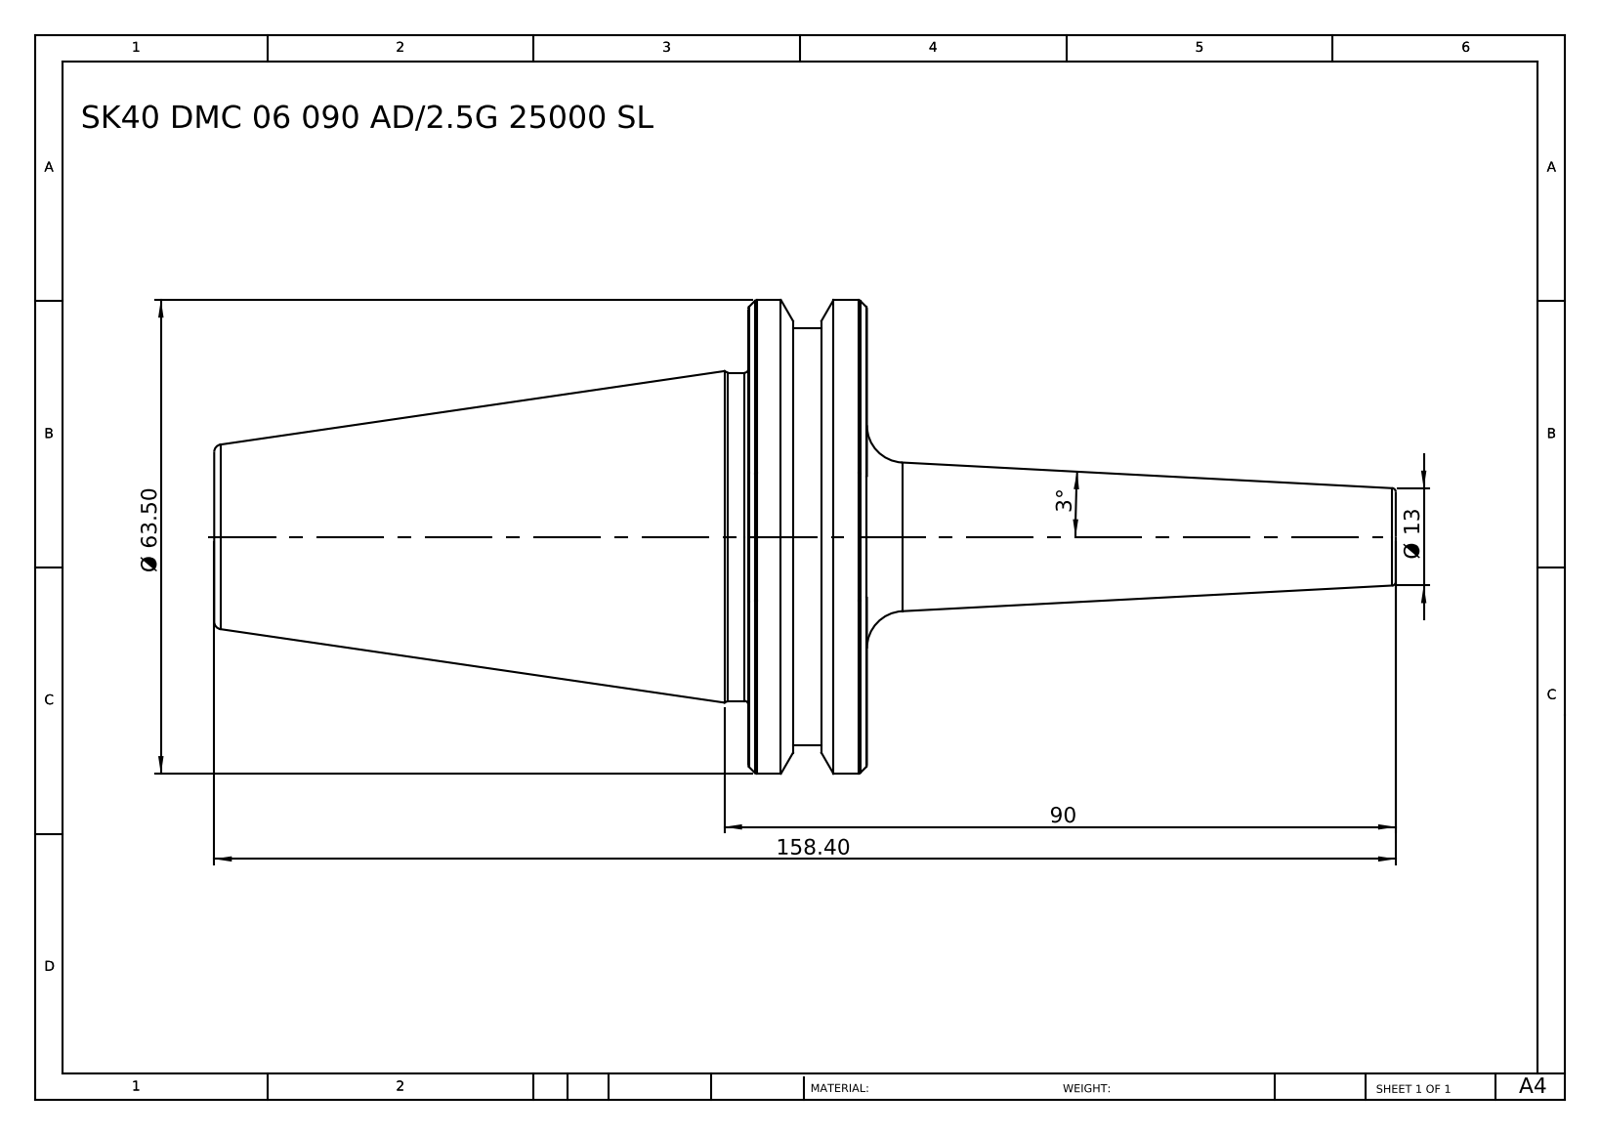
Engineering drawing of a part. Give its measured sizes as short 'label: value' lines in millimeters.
name: SK 40 DMC 06 090 AD-2.5G 25000 SL
written by: SolidWorks 2014 (CONFIG_CONTROL_DESIGN)
unit: mm
bodies: 1 solid, 64 faces (6 planar, 8 cylindrical, 50 other)
size: 158.4 × 63.5 × 63.5
volume: 133 248 mm³; area: 20 341 mm²
bosses: 1× ⌀63.5, 1× ⌀56, 1× ⌀44
face distances: 15.9, 87.5, 71.6, 6.1, 9.8, 81.4, 9.9, 3.8, 6, 77.6
